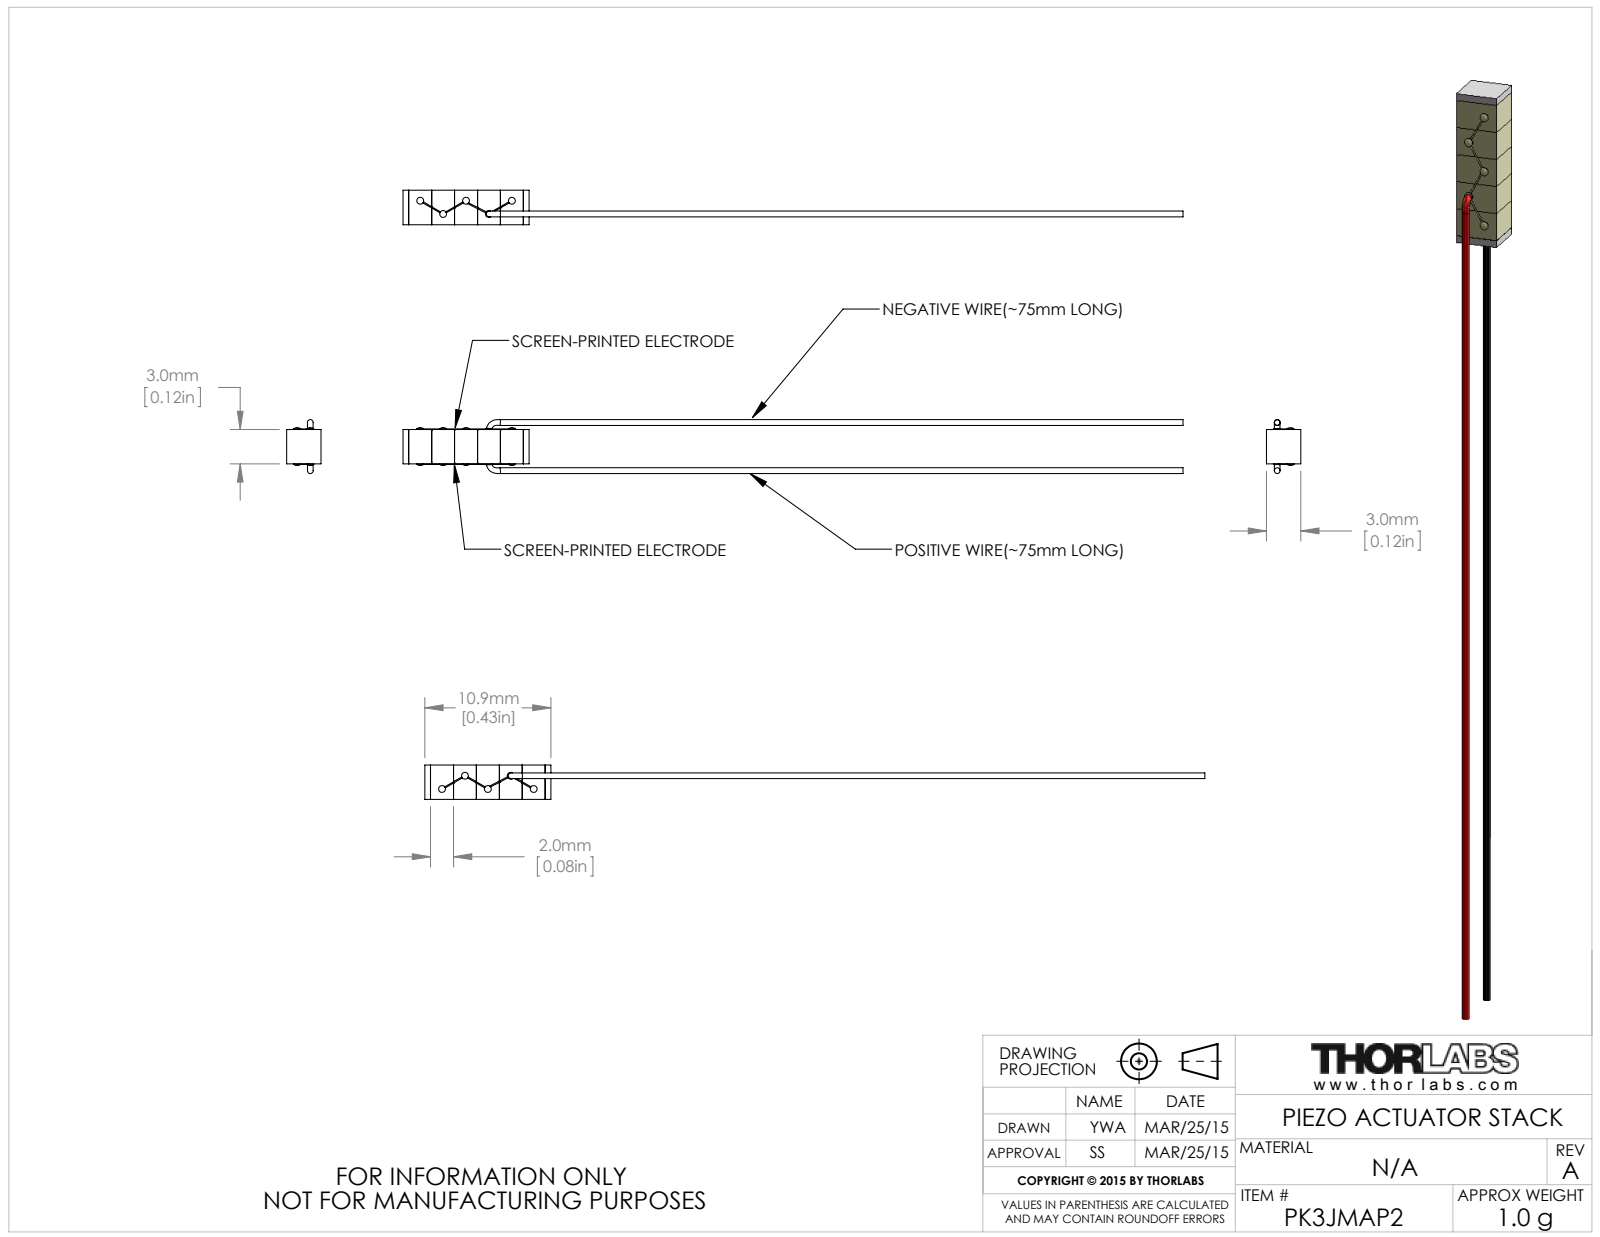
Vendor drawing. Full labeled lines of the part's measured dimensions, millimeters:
Part name (STEP PRODUCT): CTN002737
STEP written by: SolidWorks 2014 (AUTOMOTIVE_DESIGN)
Units: millimetres
Bodies: 3 solids, 124 faces (50 planar, 46 cylindrical, 28 other)
Overall size (bounding box): 68.1 × 4.72 × 3
Volume: 124 mm³ · Surface area: 452 mm²
Round bosses / shafts (diameter × count): ⌀0.6 ×5
Main face-to-face distances: 2, 3, 4, 6, 8, 0.5, 10.51, 2.51, 4.51, 6.51
